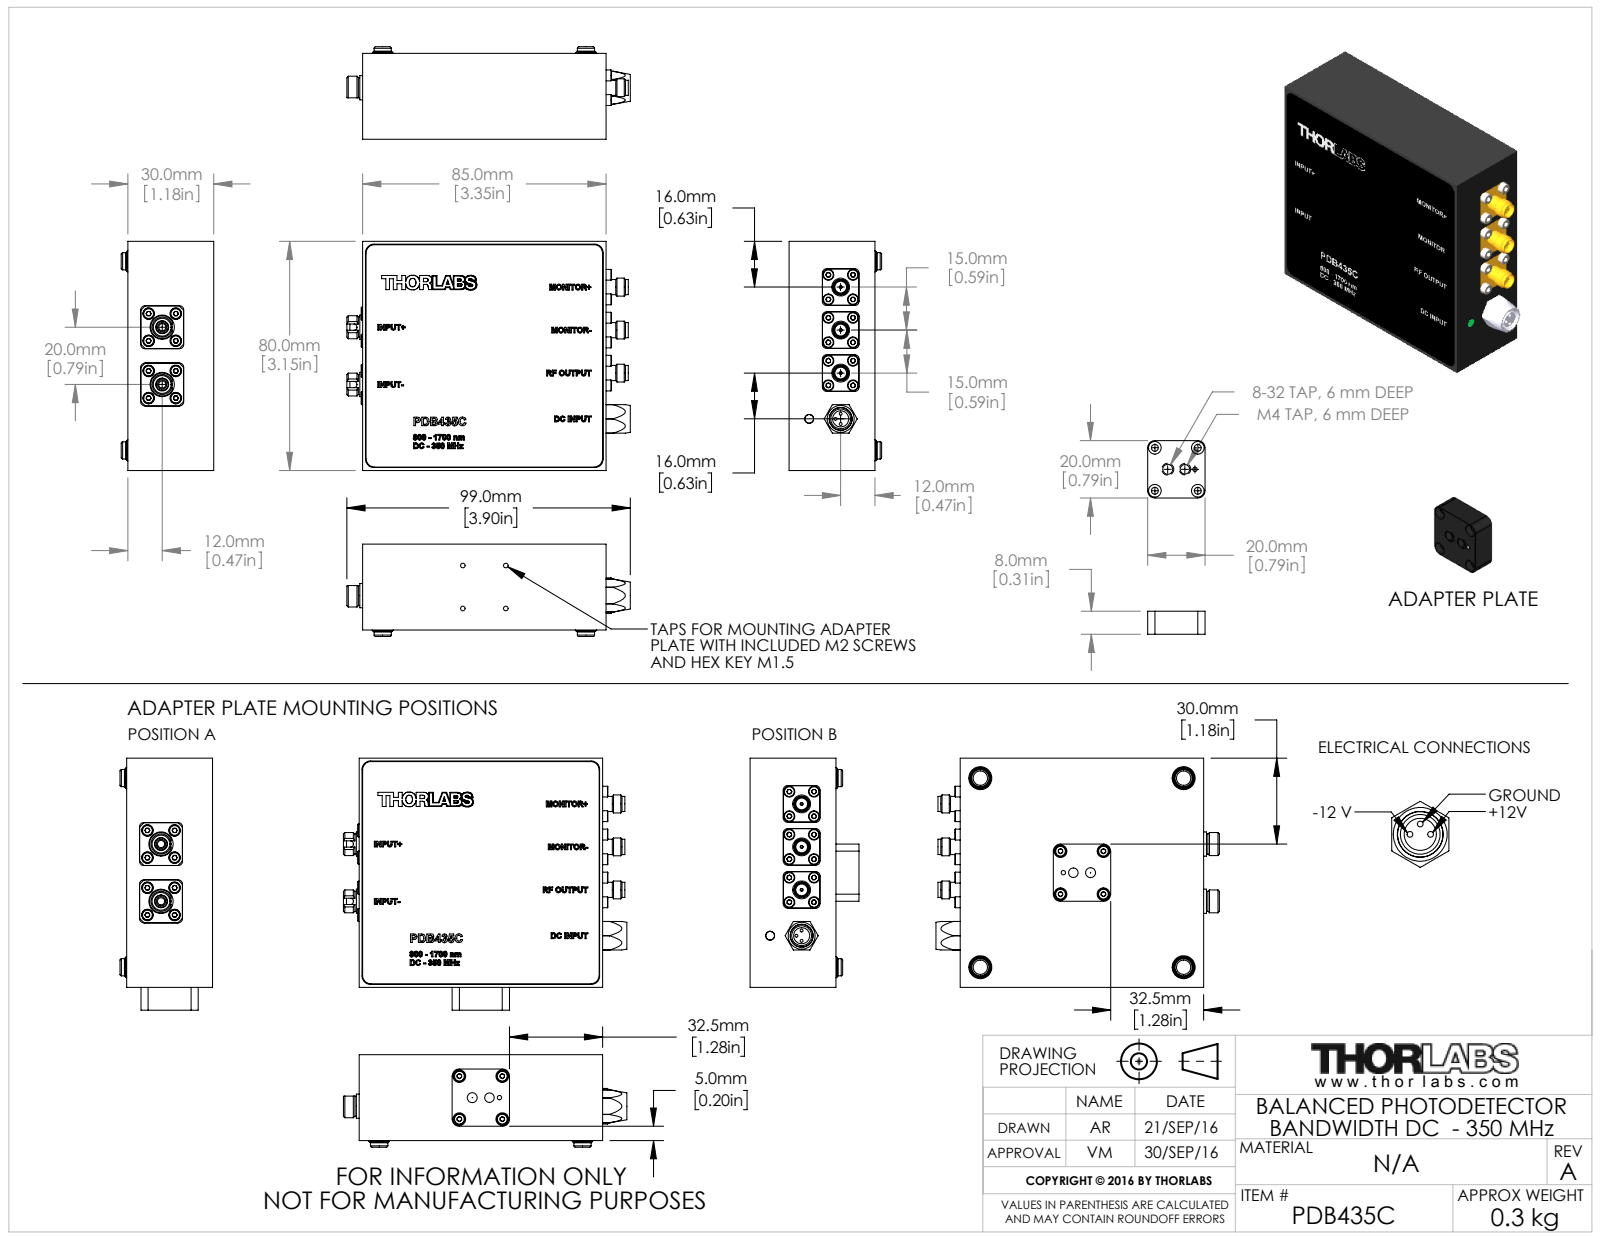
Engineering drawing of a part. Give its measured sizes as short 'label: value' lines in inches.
name: MTN005476-E0W
written by: SolidWorks 2014 (AUTOMOTIVE_DESIGN)
unit: in
bodies: 90 solids, 3044 faces (1746 planar, 584 cylindrical, 714 other)
size: 3.898 × 3.465 × 1.496
volume: 5.353 in³; area: 89.6 in²
holes: 38× ⌀0.063, 12× ⌀0.102, 8× ⌀0.087, 8× ⌀0.094, 8× ⌀0.157, 8× ⌀0.173, 6× ⌀0.04, 5× ⌀0.315, 3× ⌀0.031, 3× ⌀0.039, 3× ⌀0.161, 3× ⌀0.165
bosses: 20× ⌀0.15, 20× ⌀0.079, 8× ⌀0.177, 8× ⌀0.098, 6× ⌀0.017, 4× ⌀0.236, 3× ⌀0.245, 3× ⌀0.209
rounds: 20× R0.059, 12× R0.118, 8× R0.098, 8× R0.197, 4× R0.039, 2× R0.374, 1× R0.226
face distances: 1.169, 0.236, 0.933, 0.217, 3.15, 0.079, 2.933, 3.346, 0.138, 3.268
hole spacings: 0.591, 0.239, 0.339, 0.374, 0.265, 0.344, 0.454, 0.508
